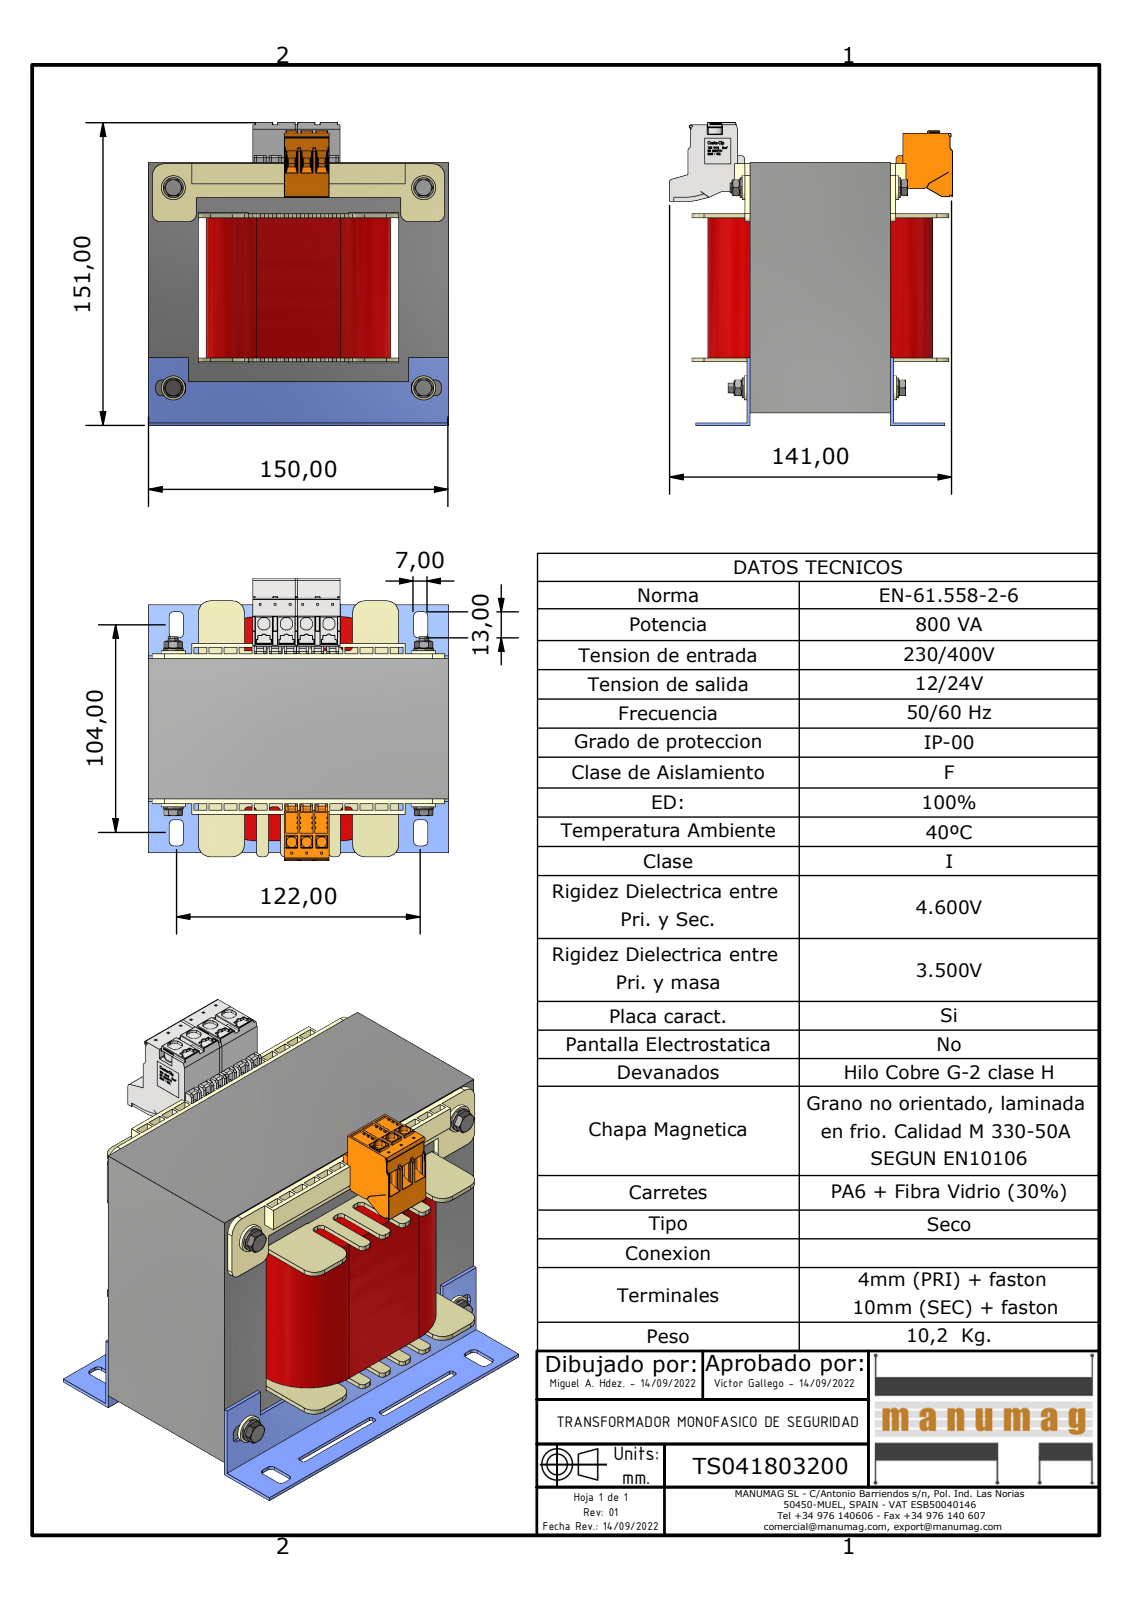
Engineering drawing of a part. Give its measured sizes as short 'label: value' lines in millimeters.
name: TS041803200; EI150 x 125 - 70 (RC50); AF50DIN; EI 150 X 125 - 70 (+7 more)
written by: Autodesk Inventor 2023 (AUTOMOTIVE_DESIGN)
unit: mm
bodies: 33 solids, 6452 faces (5206 planar, 883 cylindrical, 363 other)
size: 151.6 × 150 × 141.2
volume: 1 600 000 mm³; area: 265 238 mm²
holes: 4× ⌀4.13, 4× ⌀5, 4× ⌀5.3, 4× ⌀8
bosses: 4× ⌀12, 4× ⌀10, 4× ⌀6.7, 4× ⌀5.9, 4× ⌀4.57
rounds: 141× R0.2, 137× R0.15, 63× R0.3, 55× R2, 24× R0.1, 22× R1, 20× R0.5, 10× R6
face distances: 25, 100, 50, 70, 125, 75, 99.5, 1.5, 25.5, 74
hole spacings: 100, 125, 160.08
